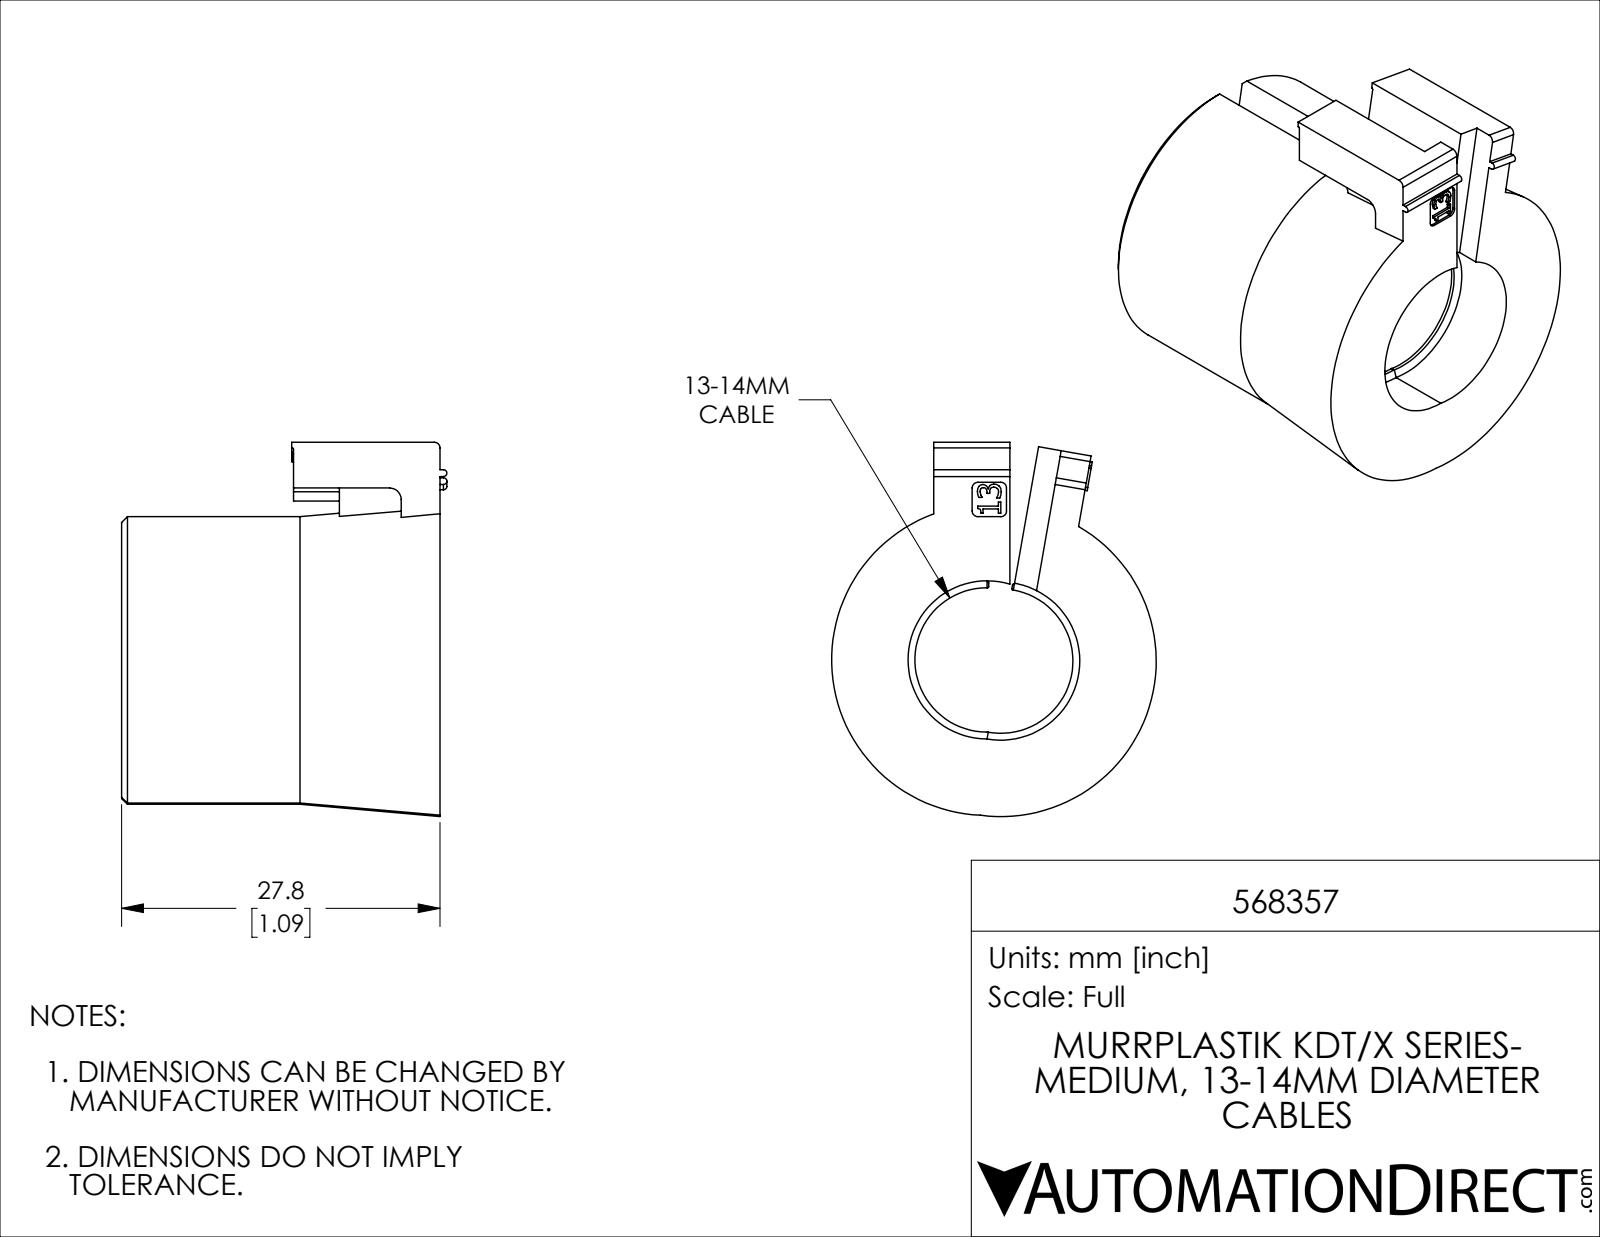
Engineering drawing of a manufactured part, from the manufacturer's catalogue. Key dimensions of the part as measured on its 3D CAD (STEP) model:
Part name (STEP PRODUCT): 568357
STEP written by: SolidWorks 2019 (CONFIG_CONTROL_DESIGN)
Units: inches
Bodies: 1 solid, 141 faces (79 planar, 29 cylindrical, 33 other)
Overall size (bounding box): 1.286 × 1.118 × 1.116
Volume: 0.643 in³ · Surface area: 7.849 in²
Partial cylindrical surfaces — rounded edges, fillets, slot ends (radius × count): R0.004 ×6, R0.02 ×6, R0.012 ×2, R0.039 ×2, R0.248 ×2, R0.272 ×2, R0.492 ×2
Main face-to-face distances: 1.094, 0.079, 0.157, 0.183, 0.183, 1.016, 0.504, 0.425, 0.591, 0.104
